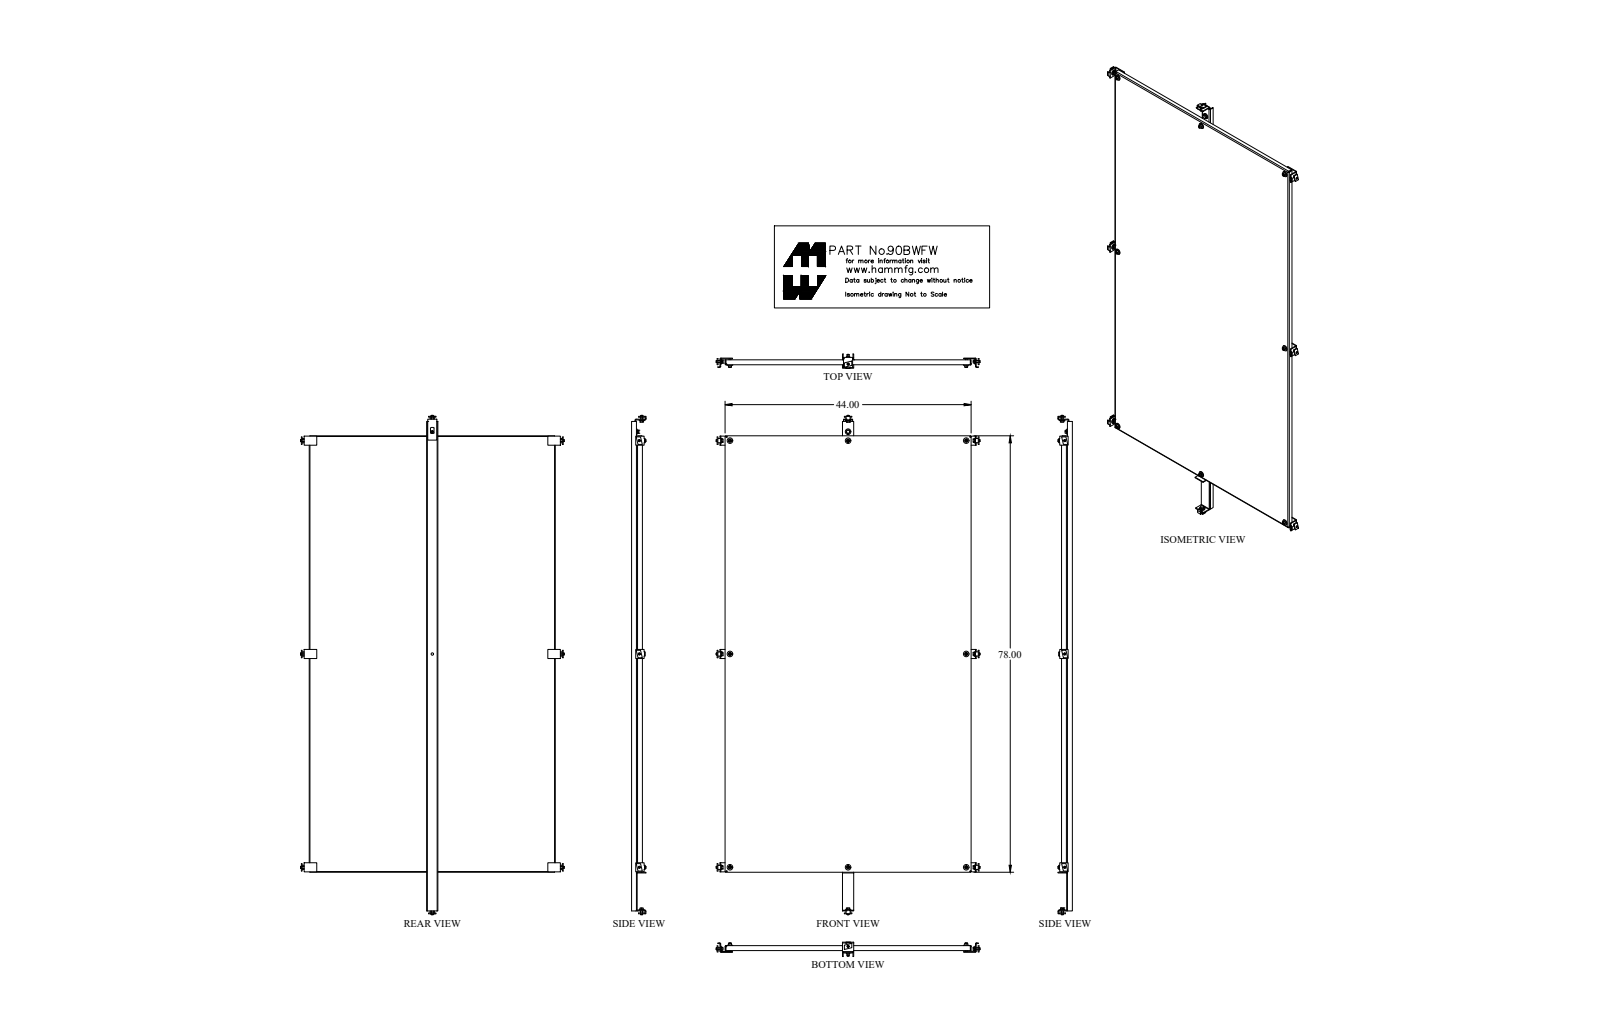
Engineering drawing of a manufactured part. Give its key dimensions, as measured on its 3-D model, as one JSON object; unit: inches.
{"part_name": "90BWFW_Default", "step_written_by": "SolidWorks 2018 (CONFIG_CONTROL_DESIGN)", "units": "inches", "bodies": {"solids": 70, "faces": 955, "planar": 552, "cylindrical": 311, "other": 92}, "overall_size": [89.27, 47.196, 2.593], "volume_in3": 500.9, "surface_area_in2": 8102, "round_holes": [[0.445, 10], [0.307, 9], [0.563, 8], [0.381, 6], [0.437, 6], [0.313, 5], [0.445, 4], [0.437, 1], [0.438, 1], [0.453, 1]], "round_bosses_or_shafts": [[1, 15], [0.375, 9], [0.65, 8], [0.33, 8], [0.672, 7], [0.375, 7]], "partial_cylinders_radius": [[0.06, 15], [0.185, 15], [0.5, 2], [0.219, 1]], "face_to_face_distances": [0.125, 1.062, 21, 0.937, 1.187, 0.125, 22.75, 22.875, 22.875, 23], "hole_center_spacings": [21.125, 43.586, 21.125, 38.125, 38.13, 42.25, 42.25, 43.587]}
